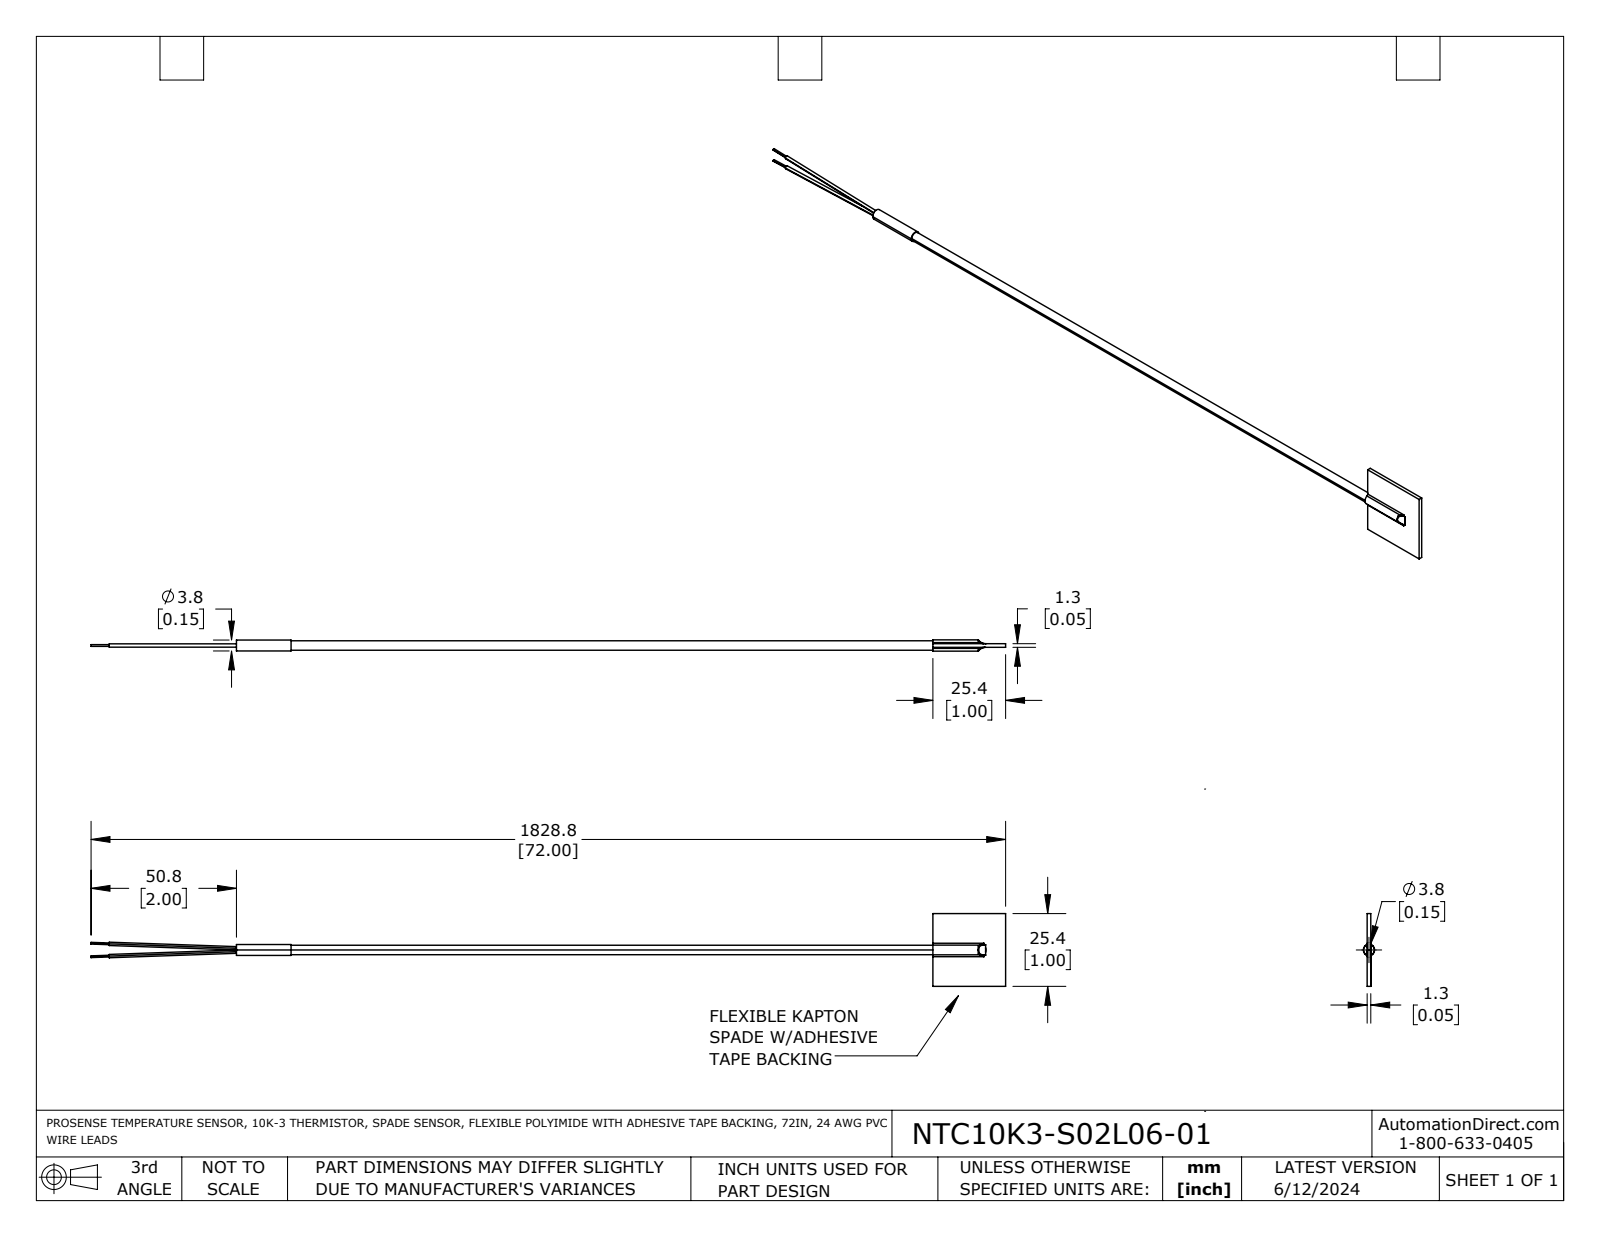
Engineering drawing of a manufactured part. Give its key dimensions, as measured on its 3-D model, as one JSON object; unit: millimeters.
{"part_name": "NTC10K3-S02L06-01", "step_written_by": "SolidWorks 2021 (AUTOMOTIVE_DESIGN)", "units": "millimeters", "bodies": {"solids": 1, "faces": 51, "planar": 19, "cylindrical": 17, "other": 15}, "overall_size": [319.4, 25.4, 3.9], "volume_mm3": 3180, "surface_area_mm2": 4767, "round_holes": [[3.3, 1]], "round_bosses_or_shafts": [[3.8, 1], [3.3, 1]], "partial_cylinders_radius": [[0.8, 4], [2, 1]], "face_to_face_distances": [1.3, 25.4, 243.2, 268.6, 19.1, 224.2, 249.6, 44.4, 63.5, 287.7]}
